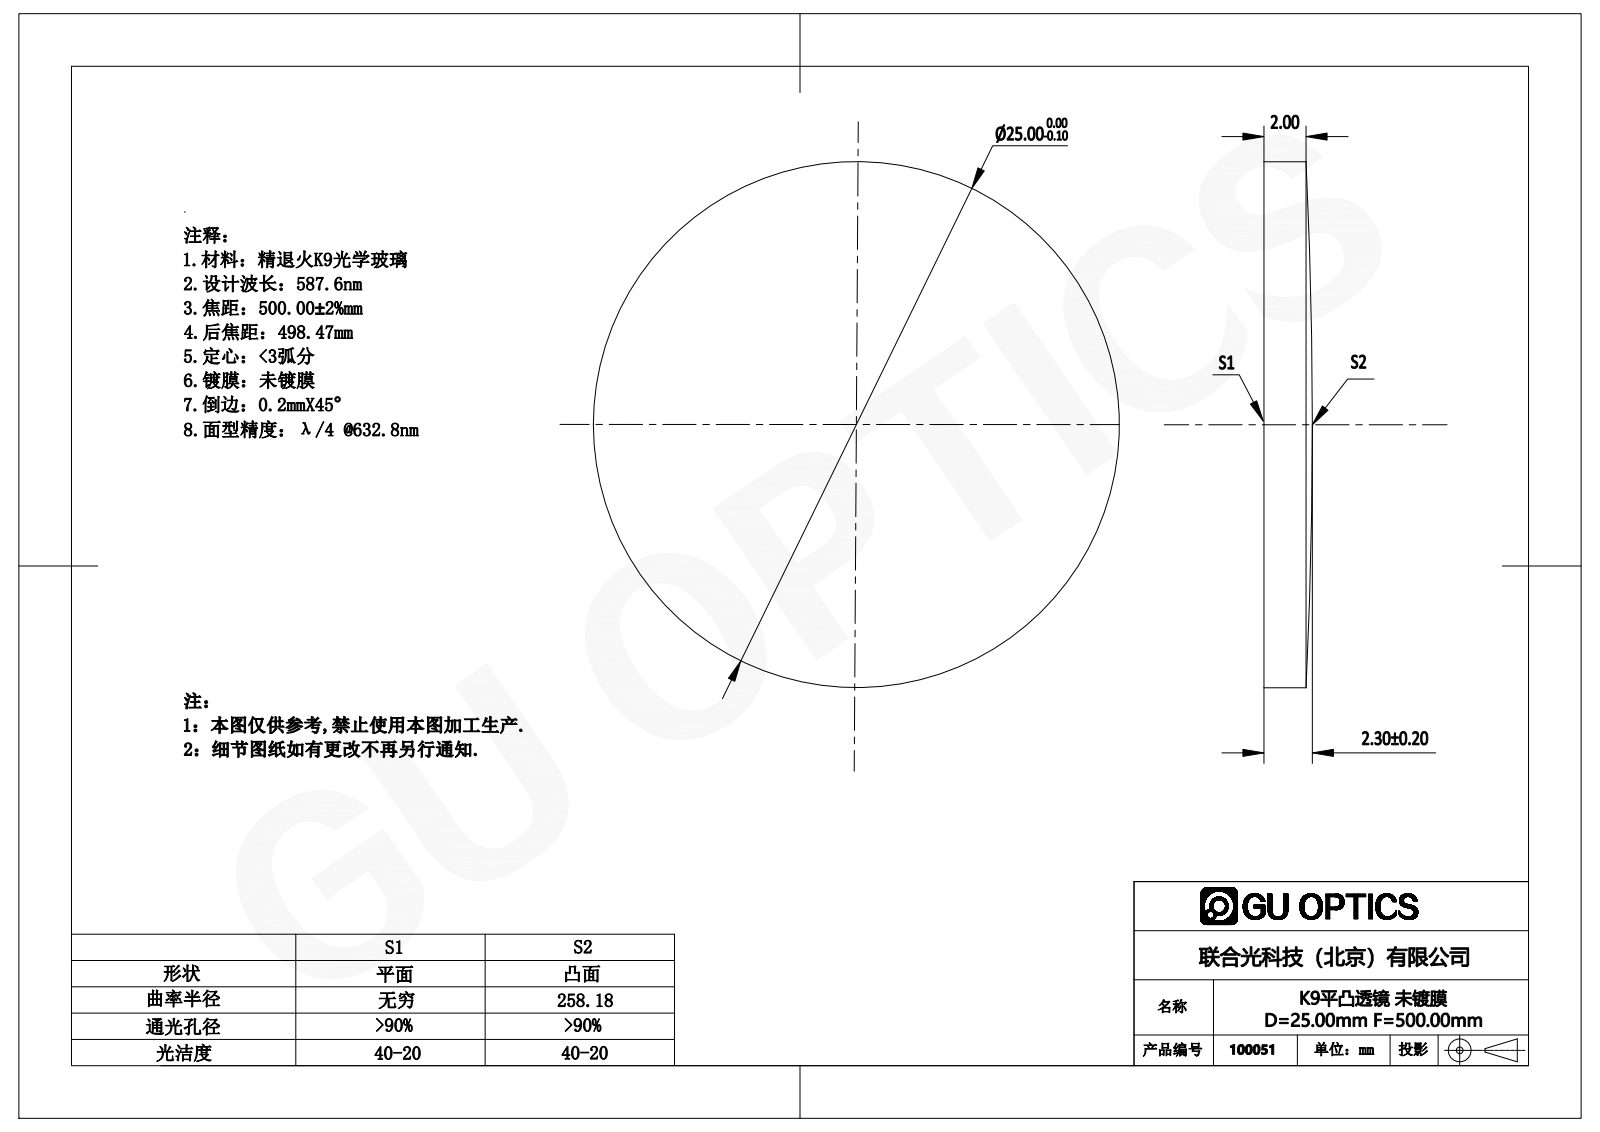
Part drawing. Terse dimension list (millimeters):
name: 100051
written by: SolidWorks 2016 (AUTOMOTIVE_DESIGN)
unit: mm
bodies: 1 solid, 5 faces (1 planar, 2 cylindrical, 2 other)
size: 25 × 25 × 2.3
volume: 1 055 mm³; area: 1 139 mm²
bosses: 1× ⌀25
